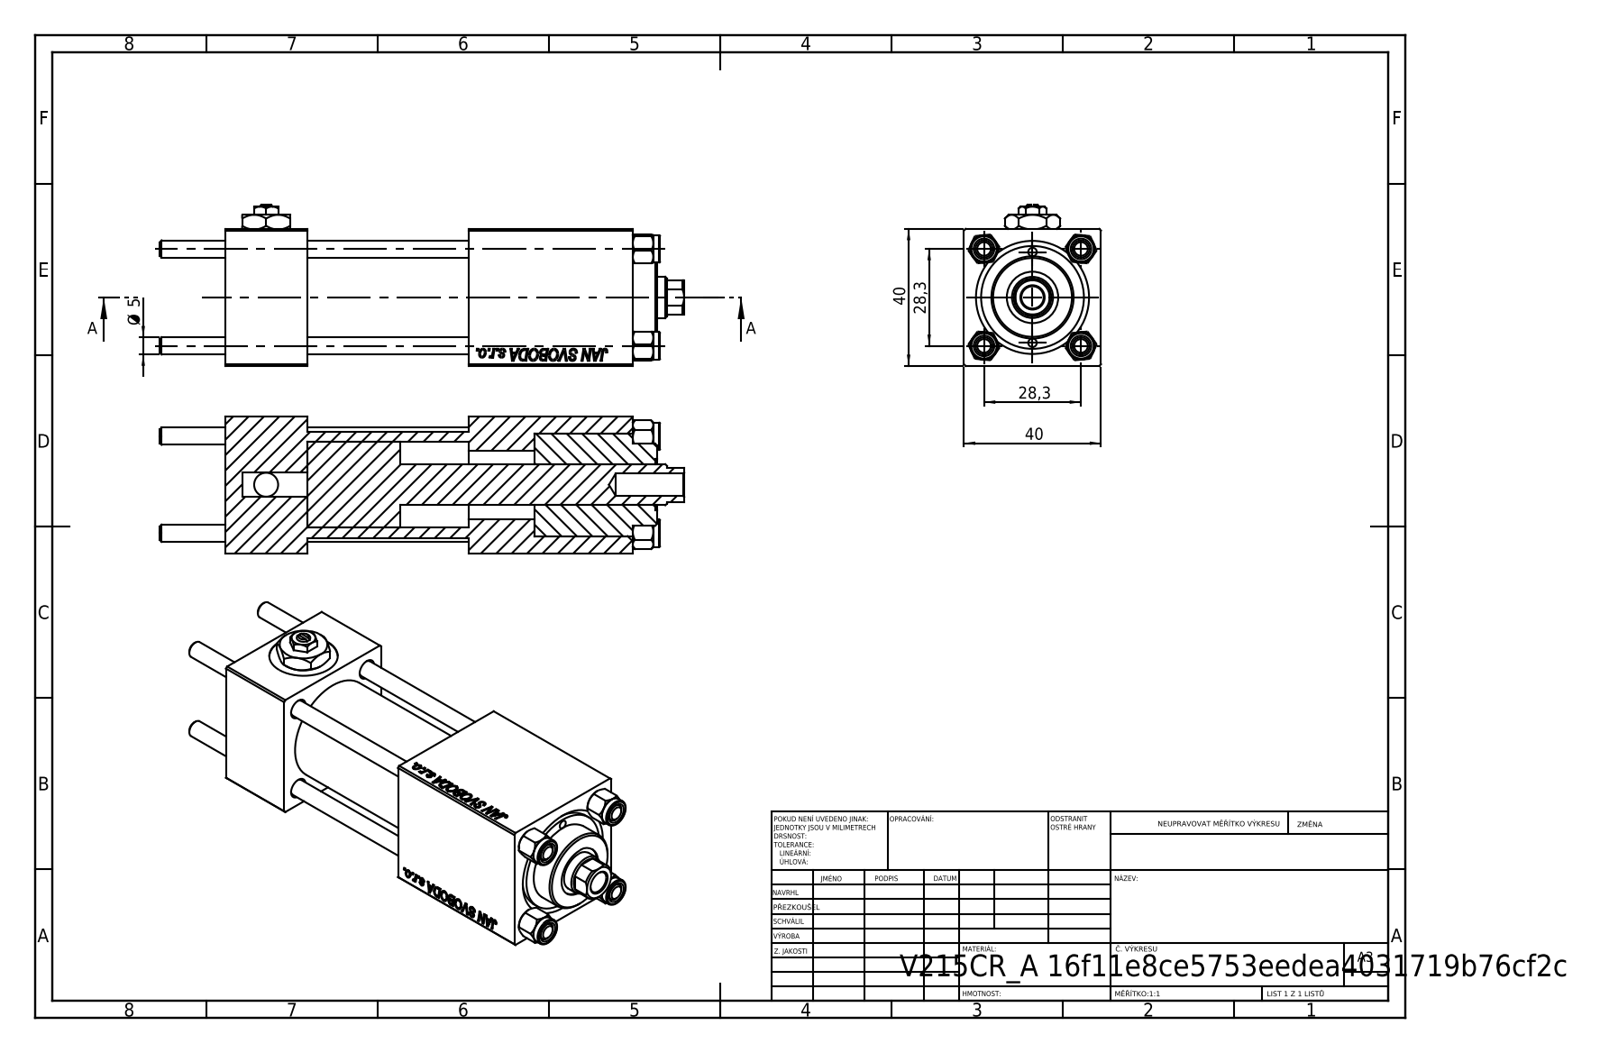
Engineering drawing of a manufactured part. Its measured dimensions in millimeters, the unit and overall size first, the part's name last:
Units: millimetres
Overall size (bounding box): 153 × 47 × 40
Round holes (diameter × count): ⌀5 ×4, ⌀20 ×3, ⌀2.5 ×2, ⌀7 ×2, ⌀13.16 ×2, ⌀6.5 ×1, ⌀12 ×1, ⌀15 ×1, ⌀25 ×1, ⌀30 ×1
Round bosses / shafts (diameter × count): ⌀8 ×4, ⌀31 ×1, ⌀24 ×1
Partial cylindrical surfaces — rounded edges, fillets, slot ends (radius × count): R5.5 ×1
Main face-to-face distances: 40, 24, 95, 90.3, 66.3, 119, 28.7, 47, 71, 19.3
Hole centre spacings: 14.18, 20.01, 28.3, 30.84, 13.25, 40.02, 26.5, 72
Volume: 144 022 mm³ · Surface area: 59 974 mm²
Bodies: 12 solids, 1190 faces (542 planar, 90 cylindrical, 558 other)
Part name (STEP PRODUCT): NUT_M5; Zatka_pro_OIL_PORT; V215_VC_A; CR025_012_A_0_G_A_G_M_020_+#_##_TYCINKA (+2 more)
STEP written by: SolidWorks 2019 (CONFIG_CONTROL_DESIGN)
